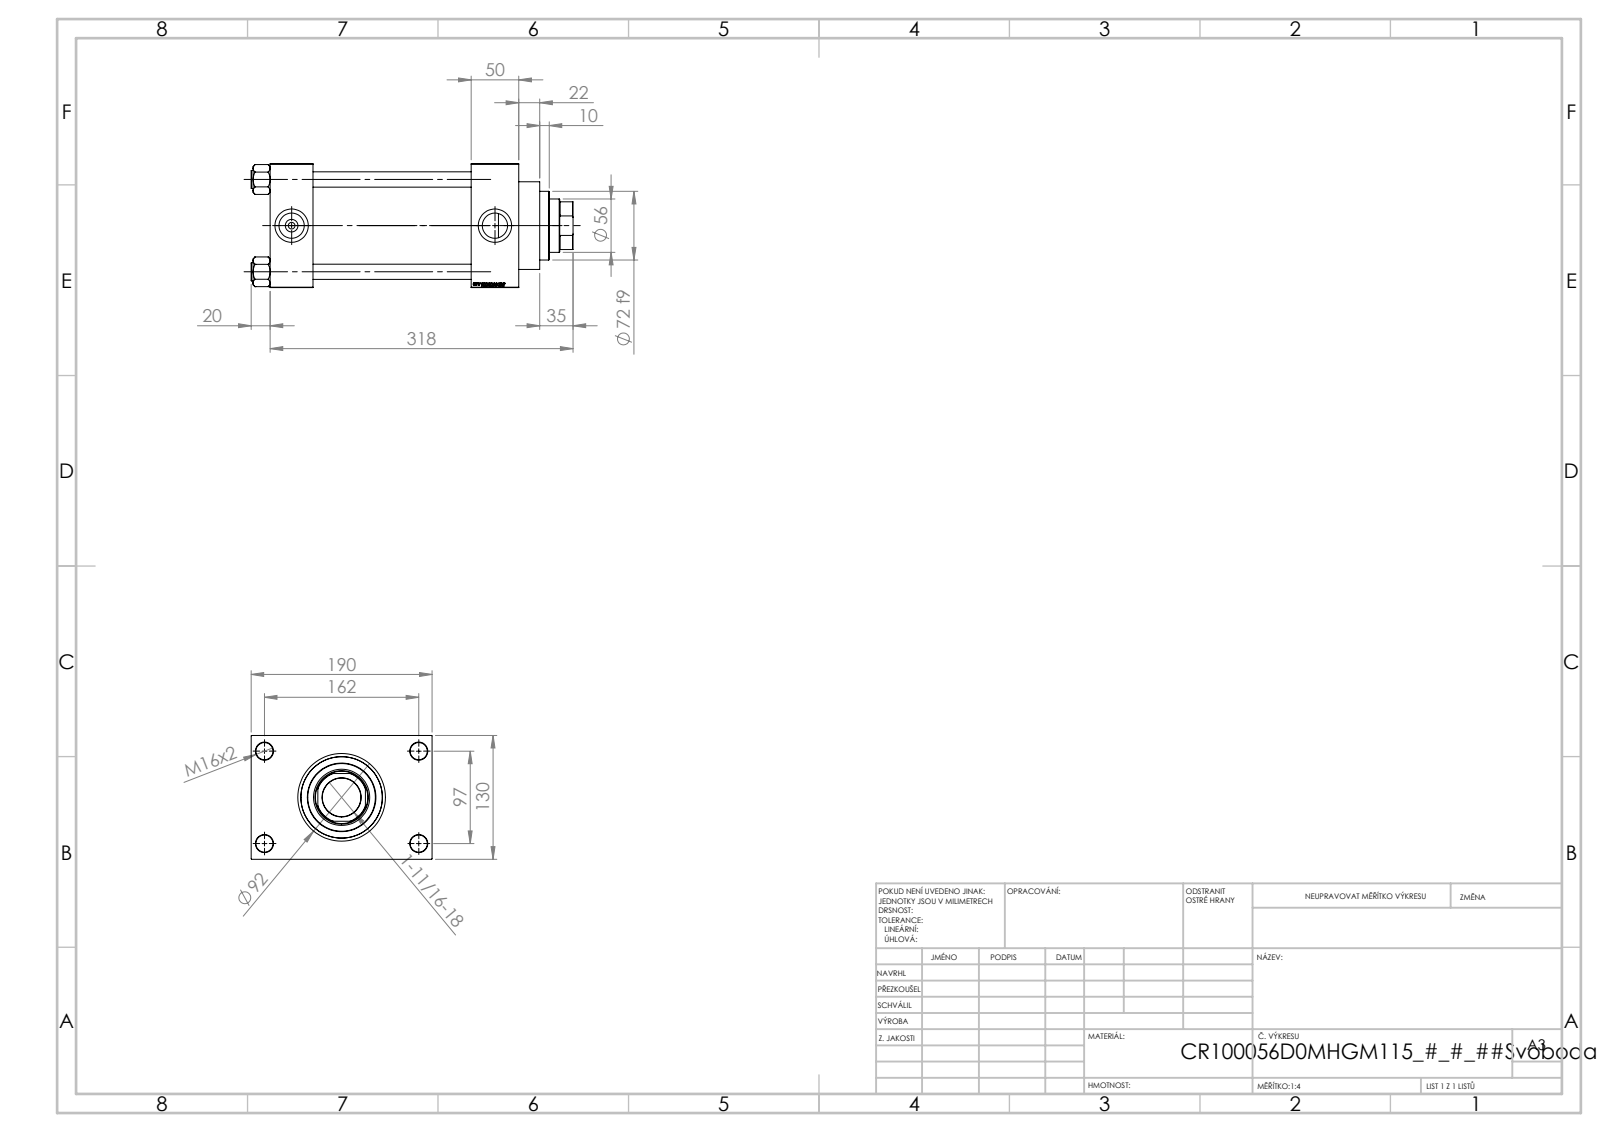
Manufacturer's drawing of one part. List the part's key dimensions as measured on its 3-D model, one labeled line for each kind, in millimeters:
Part name (STEP PRODUCT): V215_VC_A; V215CR_D_Body; V215CR_D_TYCINKA; NUT_M5_D (+1 more)
STEP written by: SolidWorks 2019 (CONFIG_CONTROL_DESIGN)
Units: millimetres
Bodies: 11 solids, 1151 faces (545 planar, 88 cylindrical, 518 other)
Overall size (bounding box): 338 × 190 × 130
Volume: 3 031 000 mm³ · Surface area: 459 658 mm²
Round holes (diameter × count): ⌀16 ×4, ⌀18 ×4, ⌀7 ×2, ⌀26.44 ×2, ⌀35 ×2, ⌀40.5 ×1, ⌀56 ×1, ⌀59 ×1, ⌀76 ×1, ⌀85.5 ×1, ⌀100 ×1
Round bosses / shafts (diameter × count): ⌀19 ×4, ⌀106 ×1, ⌀92 ×1, ⌀72 ×1
Partial cylindrical surfaces — rounded edges, fillets, slot ends (radius × count): R27 ×1
Main face-to-face distances: 130, 50, 45, 211, 166, 261, 216, 30, 160, 190
Hole centre spacings: 32.55, 68.52, 94.41, 96.9, 102.27, 129.45, 161.73, 97
